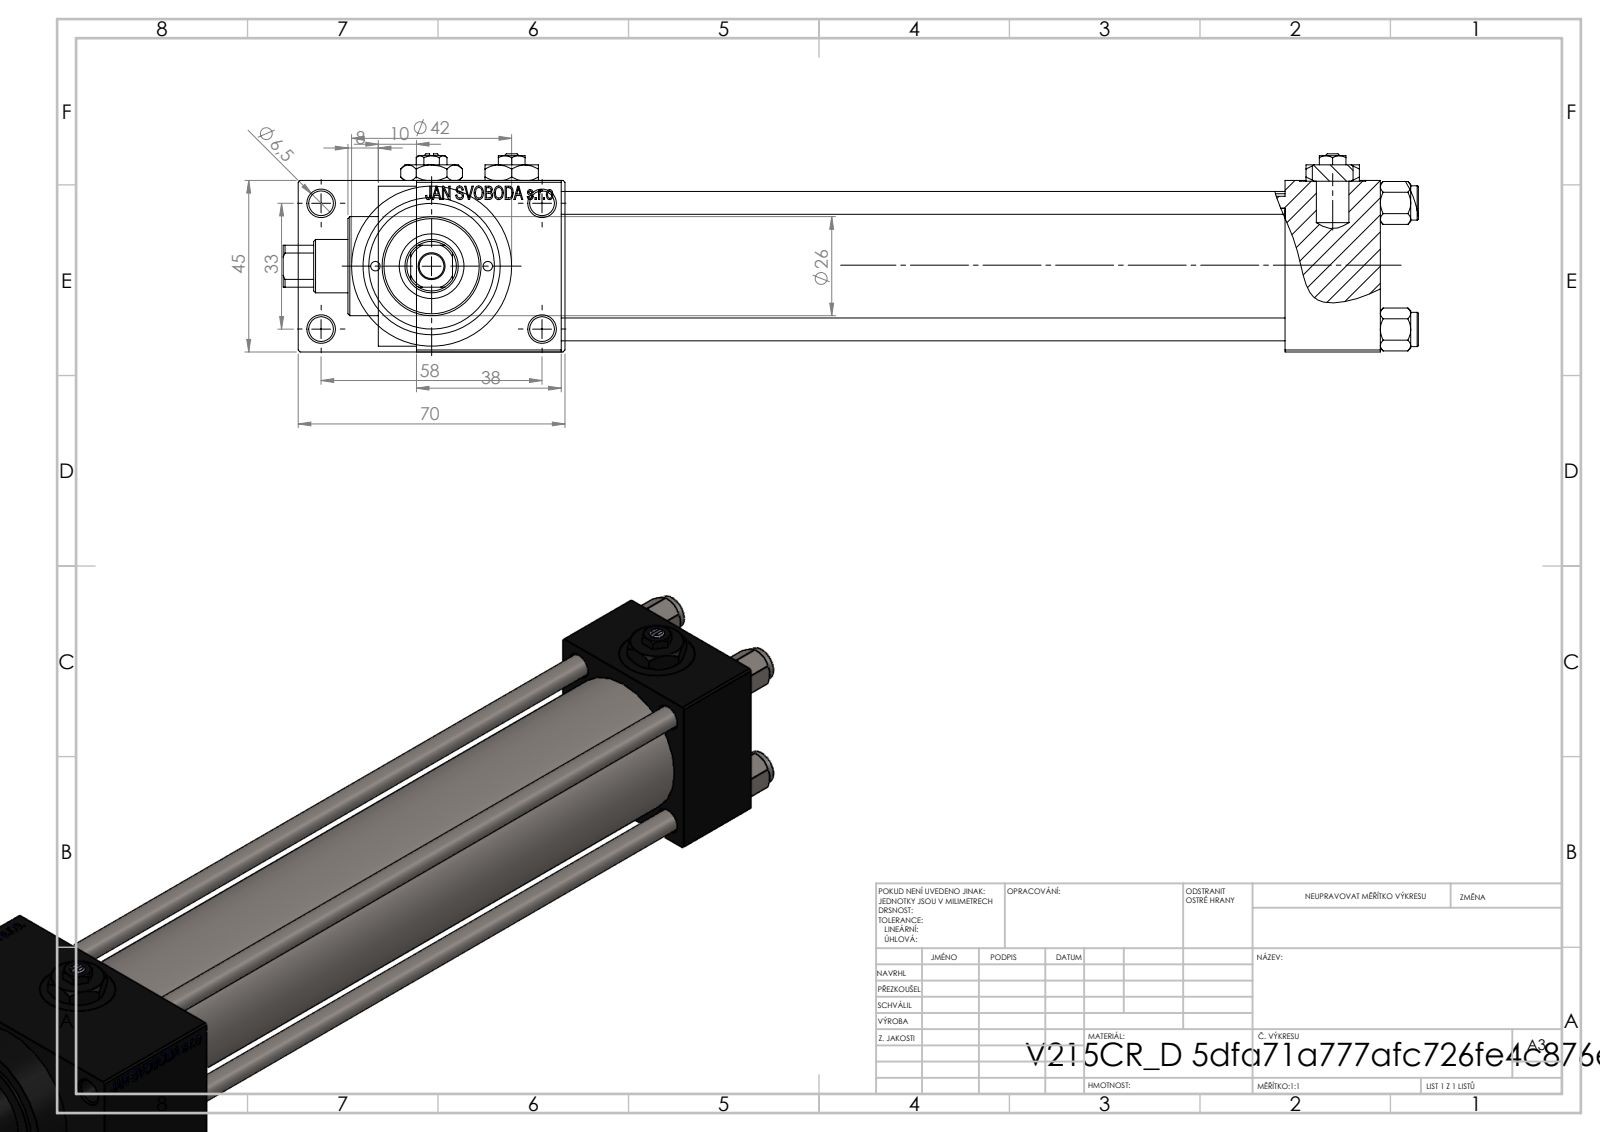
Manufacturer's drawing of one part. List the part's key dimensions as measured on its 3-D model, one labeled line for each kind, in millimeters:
Part name (STEP PRODUCT): V215_VC_A; V215CR_D_TYCINKA; Zatka_pro_OIL_PORT; V215CR_D_Body (+2 more)
STEP written by: SolidWorks 2019 (CONFIG_CONTROL_DESIGN)
Units: millimetres
Bodies: 13 solids, 1209 faces (544 planar, 103 cylindrical, 562 other)
Overall size (bounding box): 298 × 70 × 52
Volume: 312 472 mm³ · Surface area: 124 620 mm²
Round holes (diameter × count): ⌀6.5 ×5, ⌀6 ×4, ⌀13.16 ×4, ⌀20 ×4, ⌀7 ×3, ⌀2.5 ×2, ⌀14 ×1, ⌀17 ×1, ⌀24 ×1, ⌀32 ×1, ⌀33 ×1
Round bosses / shafts (diameter × count): ⌀9 ×4, ⌀42 ×1, ⌀38 ×1, ⌀26 ×1
Partial cylindrical surfaces — rounded edges, fillets, slot ends (radius × count): R6.5 ×1
Main face-to-face distances: 45, 25, 12.5, 190, 215, 57.5, 228, 38, 253, 70
Hole centre spacings: 12.4, 16.7, 21.8, 23.48, 33.2, 33.37, 35.35, 35.47
